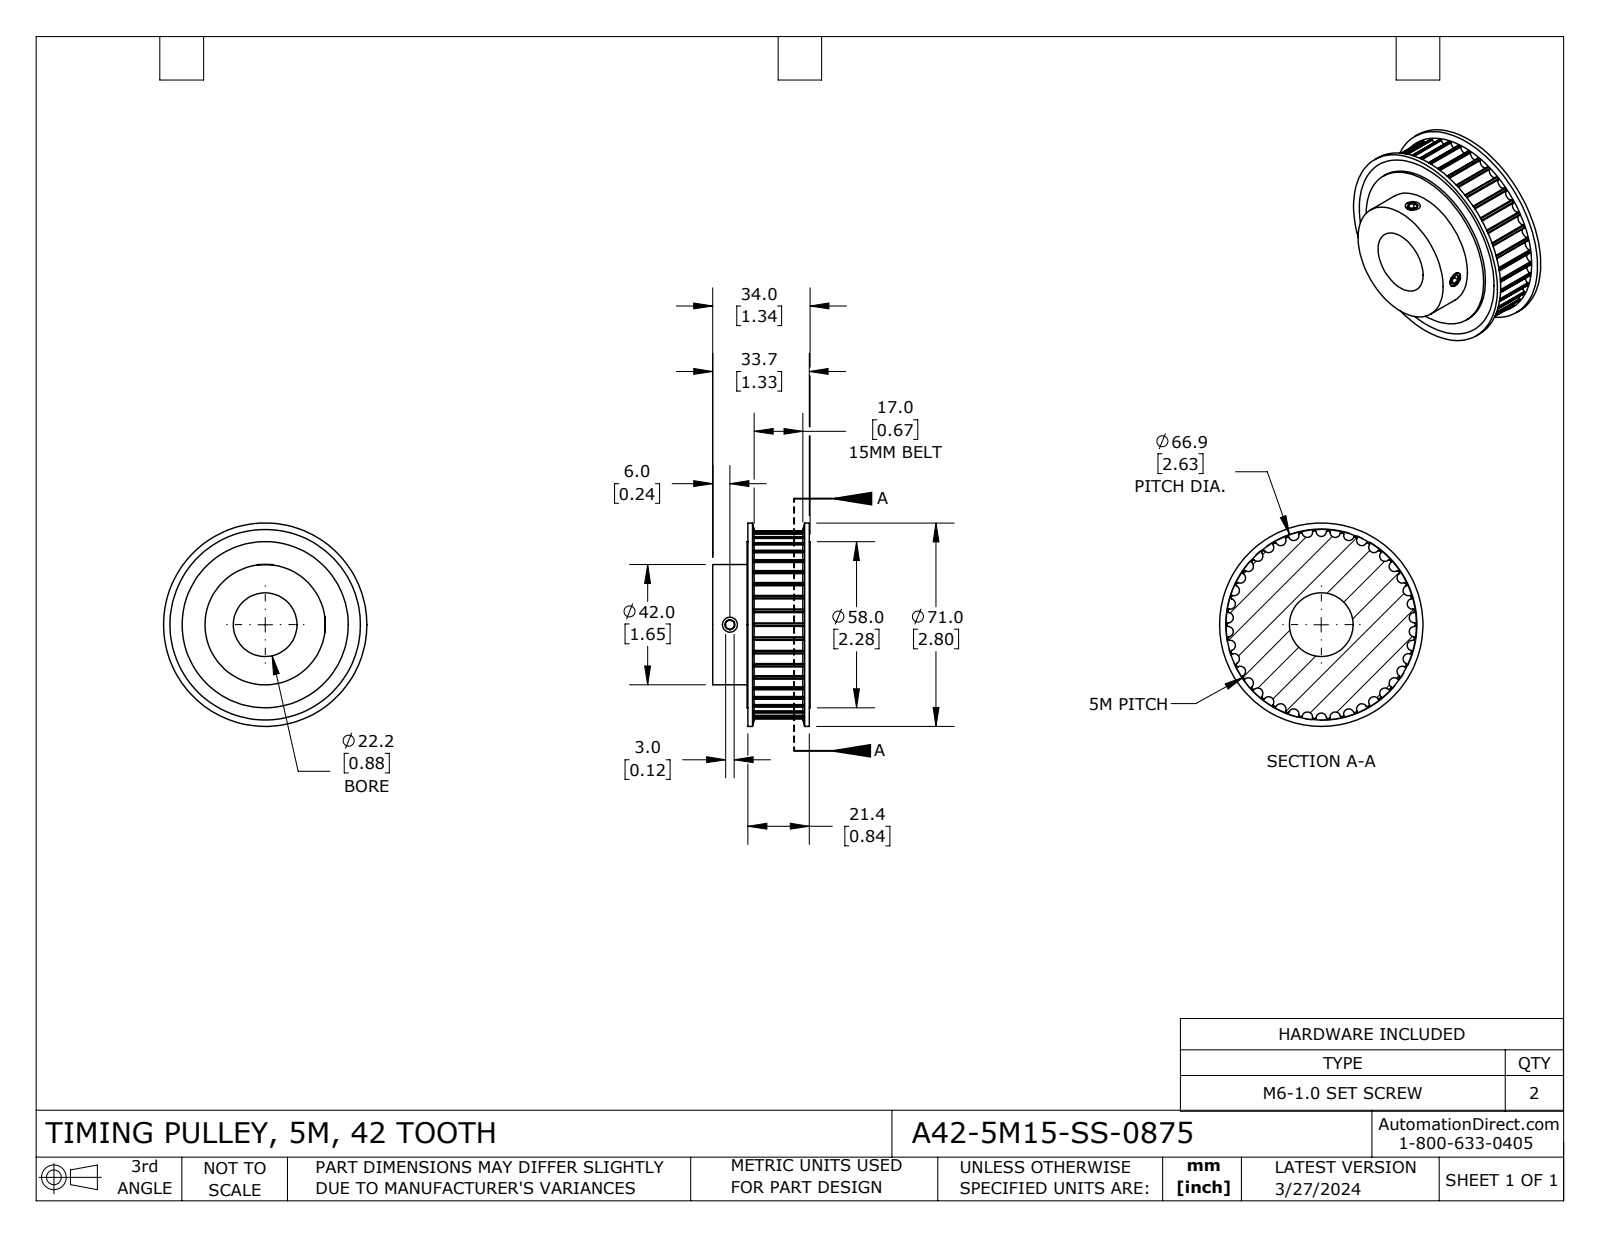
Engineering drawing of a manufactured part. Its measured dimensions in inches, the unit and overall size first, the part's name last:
Units: inches
Overall size (bounding box): 2.795 × 2.795 × 1.339
Round holes (diameter × count): ⌀0.197 ×2, ⌀0.875 ×1, ⌀2.283 ×1
Round bosses / shafts (diameter × count): ⌀0.236 ×2, ⌀2.795 ×1, ⌀1.654 ×1
Partial cylindrical surfaces — rounded edges, fillets, slot ends (radius × count): R0.012 ×84, R0.072 ×42, R1.293 ×1
Main face-to-face distances: 0.098, 0.768, 0.035, 0.831, 0.063, 0.732, 0.669, 0.866, 1.339, 1.24
Volume: 4.523 in³ · Surface area: 34.96 in²
Bodies: 5 solids, 292 faces (25 planar, 233 cylindrical, 34 other)
Part name (STEP PRODUCT): A42-5M15-SS-0875
STEP written by: SolidWorks 2021 (CONFIG_CONTROL_DESIGN)
